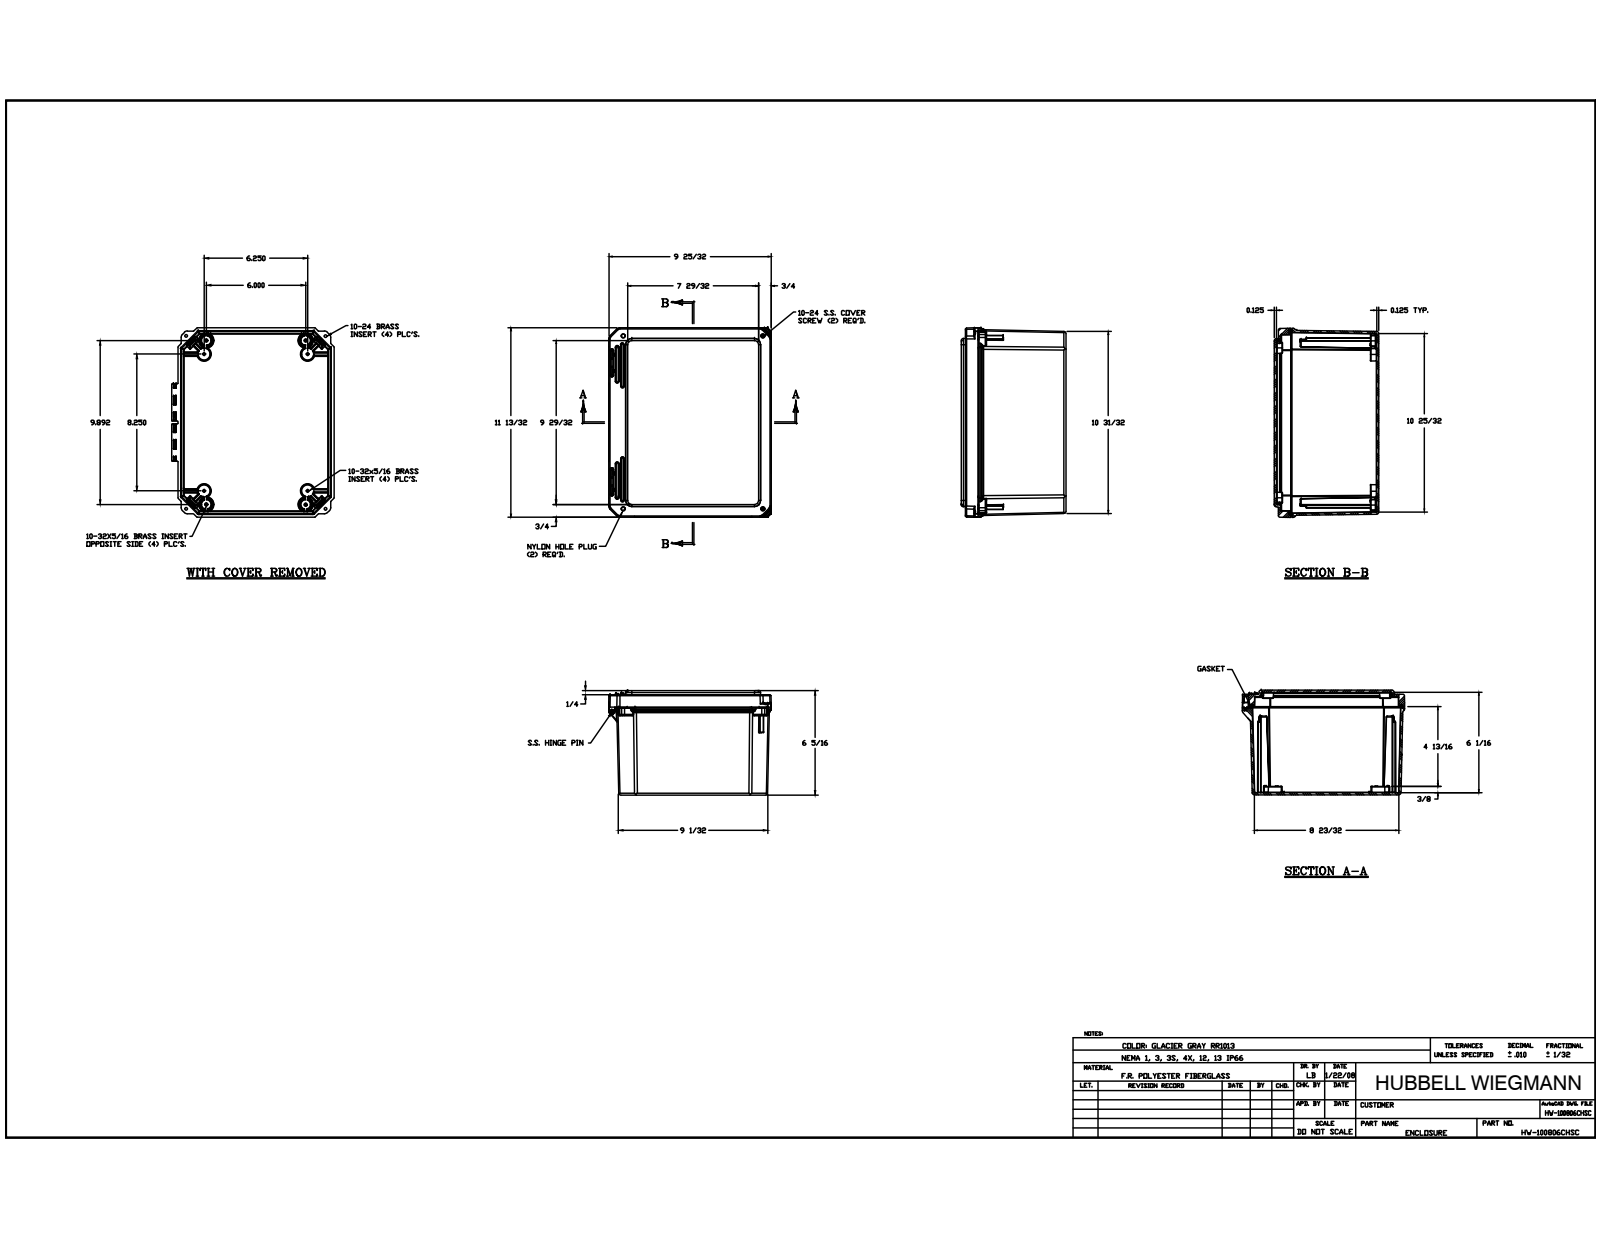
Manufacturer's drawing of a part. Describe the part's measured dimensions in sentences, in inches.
The part is named "DS100806BOX; BRASS INSERT-(; BRASS INSERT-(_1; BRASS INSERT-(_2 (+8 more)". Its 3-D file was written by "Autodesk Inventor 2014 (AUTOMOTIVE_DESIGN)". It is 29 solids with 2233 faces: 703 planar, 864 cylindrical and 666 other. Overall it measures 11.423 by 9.8 by 6.31 inches. Its volume is 70.79 cubic inches and its surface area 989.8 square inches. Round holes: 16 of diameter 0.156, 8 of diameter 0.152, 4 of diameter 0.252, 4 of diameter 0.253, 2 of diameter 0.15, 2 of diameter 0.219, 2 of diameter 0.227, 2 of diameter 0.313, 1 of diameter 0.137. Round bosses or shafts: 16 of diameter 0.246, 4 of diameter 0.87, 2 of diameter 0.45, 2 of diameter 0.435, 2 of diameter 0.209, 2 of diameter 0.199, 1 of diameter 0.135. Partial cylindrical surfaces (rounded edges, fillets, slot ends): 203 of radius 0.01, 84 of radius 0.02, 80 of radius 0.005, 45 of radius 0.03, 26 of radius 0.063, 24 of radius 0.03, 24 of radius 0.09, 24 of radius 0.096. The main face-to-face distances are 0.125, 6.185, 0.127, 0.126, 6.31, 6.061, 0.25, 5.935, 0.125, 6.06. The hole center spacings are 9.399, 11.874, 12.457, 1.535, 6.18, 7.416, 8.25, 0.83.
